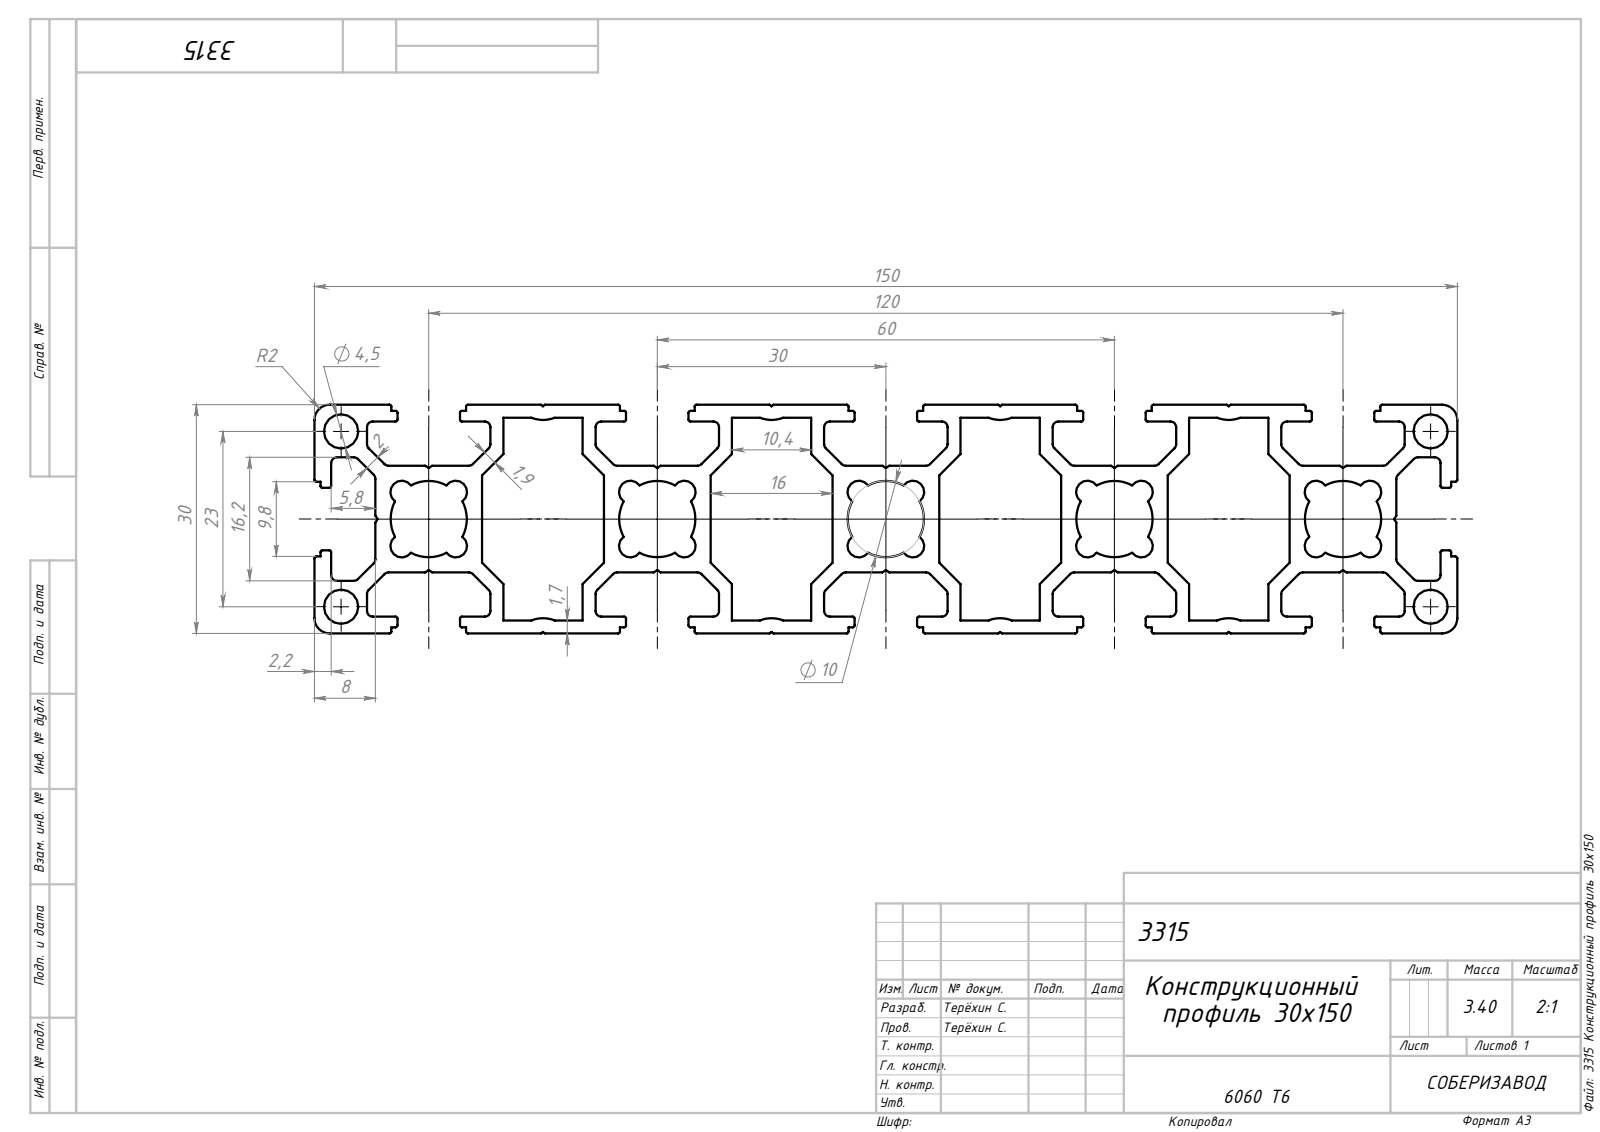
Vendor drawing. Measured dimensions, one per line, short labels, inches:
name: 3315 Конструкционный профиль 30х150
written by: SolidWorks 2022 (AUTOMOTIVE_DESIGN)
unit: in
bodies: 1 solid, 510 faces (290 planar, 220 cylindrical, 0 other)
size: 39.37 × 5.906 × 1.181
volume: 76.95 in³; area: 1 962 in²
holes: 4× ⌀0.177
rounds: 76× R0.01, 72× R0.03, 20× R0.059, 8× R0.157, 5× R0.197, 4× R0.079
face distances: 1.181, 0.866, 0.315, 2.362, 0.551, 0.835, 0.661, 1.071, 0.11, 0.52
hole spacings: 0.906, 5.63, 5.702
